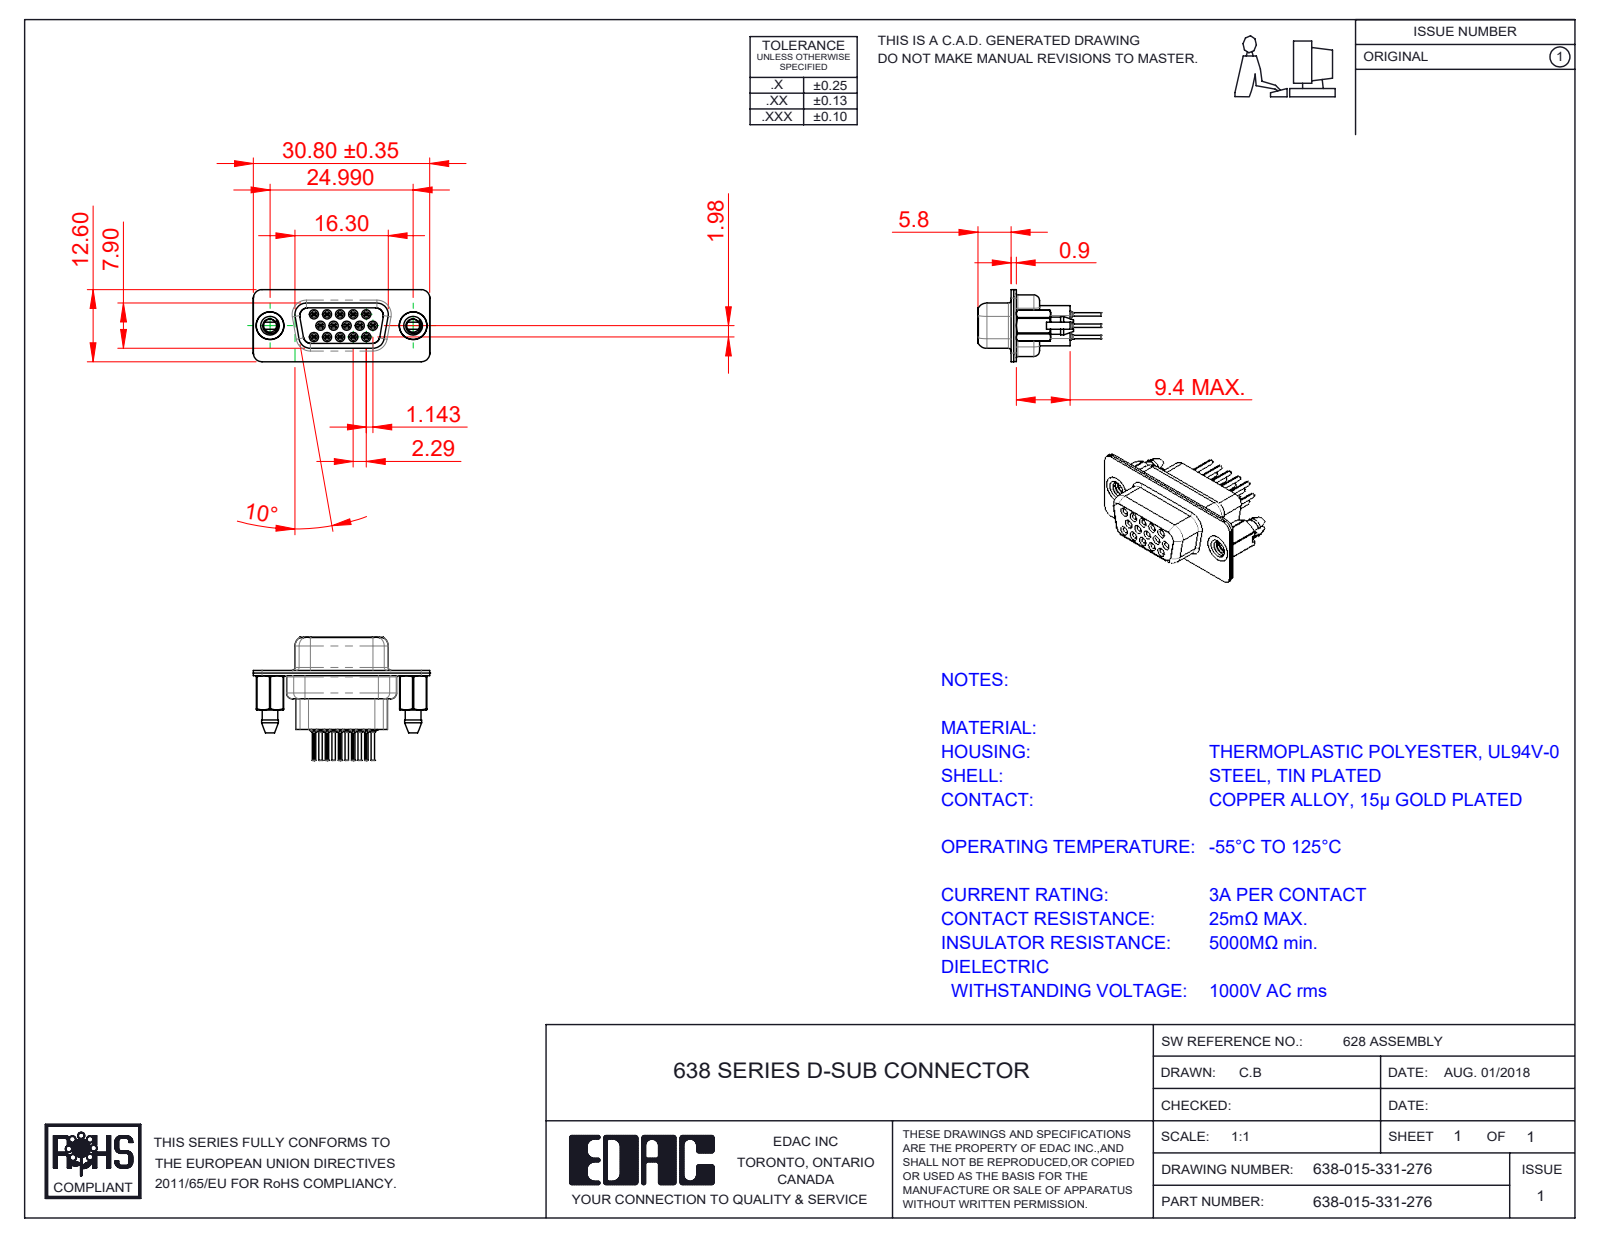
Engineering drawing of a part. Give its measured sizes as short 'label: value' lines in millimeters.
name: 638 Contact Row 1_31; 638 Shell Rear_15 Contacts; 638 Contact Row 2_31; 638 Shell Front_15 Contacts (+4 more)
written by: SolidWorks 2020 (CONFIG_CONTROL_DESIGN)
unit: mm
bodies: 20 solids, 2198 faces (564 planar, 664 cylindrical, 970 other)
size: 30.81 × 21.5 × 12.6
volume: 1 996 mm³; area: 6 817 mm²
holes: 15× ⌀0.2, 15× ⌀0.8, 15× ⌀1, 15× ⌀1.1, 15× ⌀1.6, 15× ⌀1.7, 15× ⌀1.8, 2× ⌀2, 2× ⌀2.26, 2× ⌀4, 2× ⌀4.05, 2× ⌀4.85
bosses: 15× ⌀2, 15× ⌀1.5, 15× ⌀1.2, 15× ⌀0.6, 2× ⌀4.95, 2× ⌀4.8
rounds: 30× R0.1, 22× R1.5, 12× R2, 10× R0.28, 8× R1.55, 5× R1.35, 4× R0.25, 4× R0.5
face distances: 0.45, 0.9, 0.4, 1.43, 6.6, 8.88, 7, 2.28, 5.8, 9.4
hole spacings: 3.96, 2.28, 4.57, 2.29, 6.05, 6.04, 6.86, 7.92
